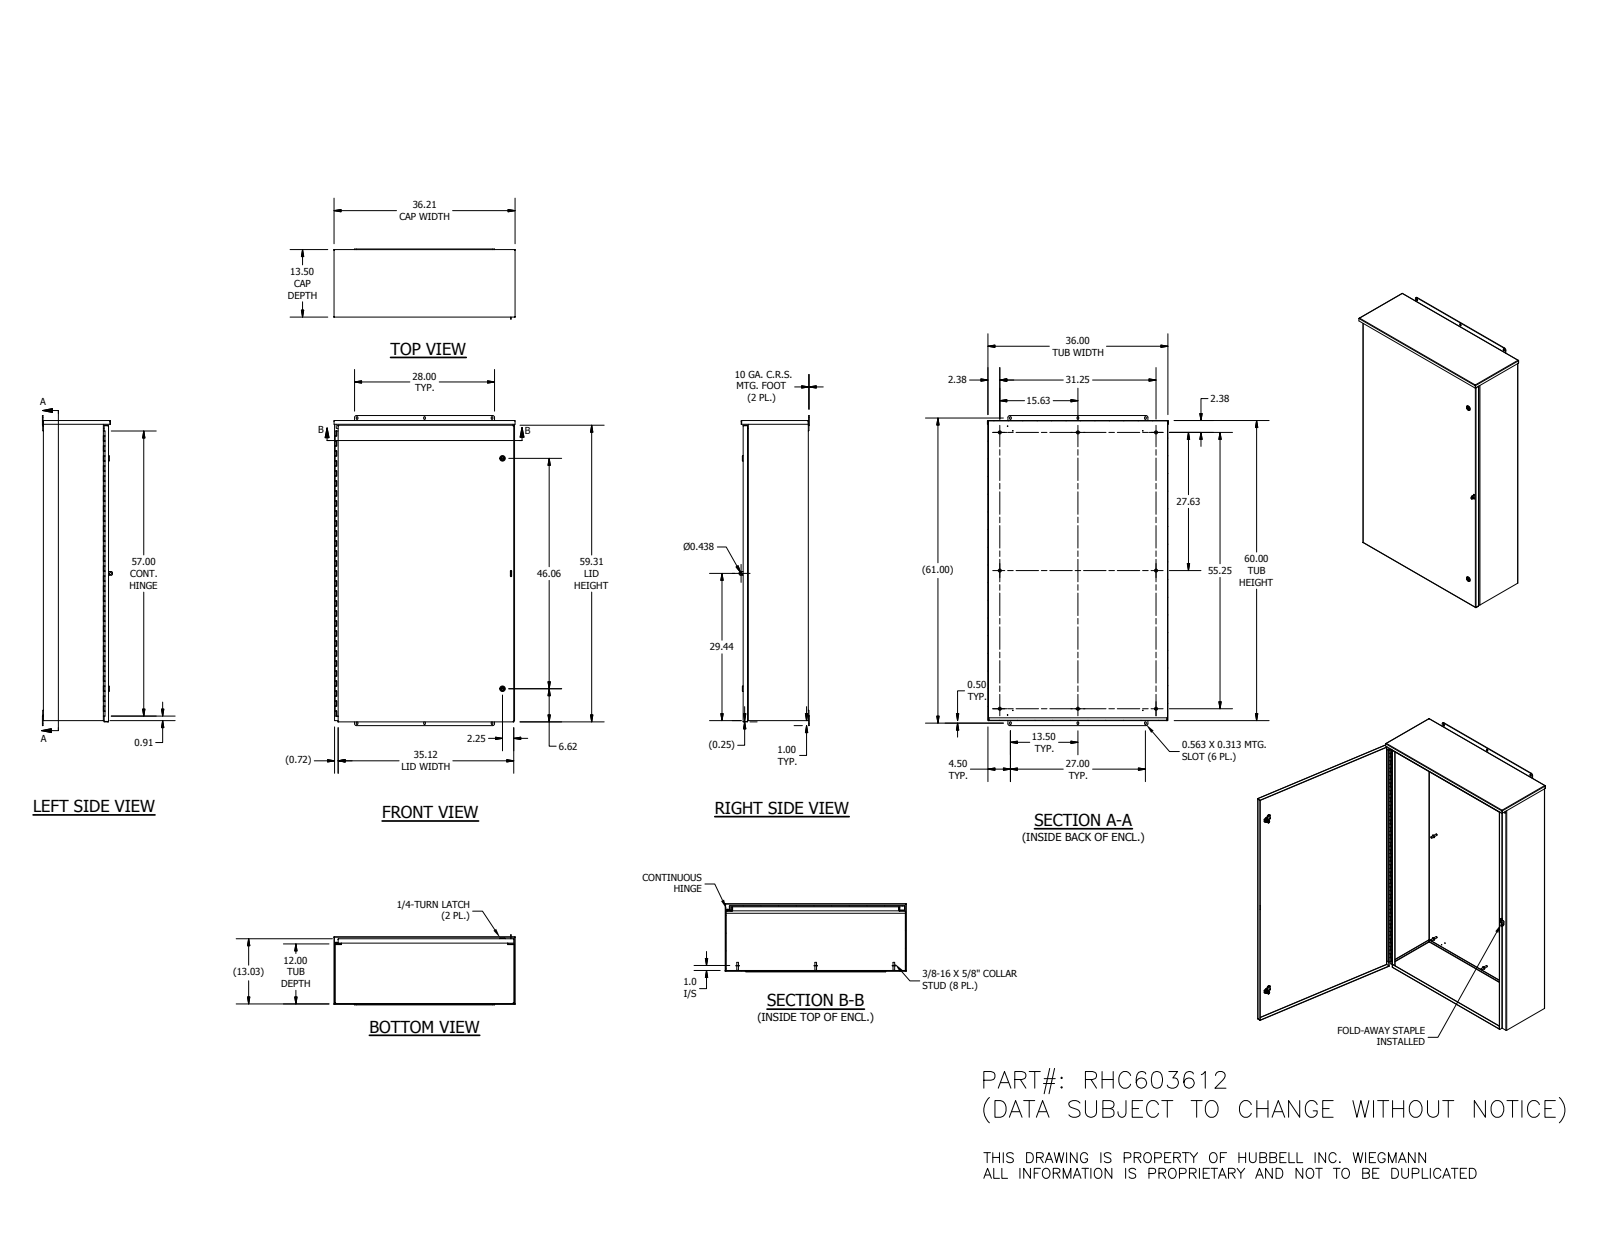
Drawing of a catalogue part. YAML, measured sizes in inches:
part_name: "RHC603612BLR; RHC36TOP; RHC3612BTM; RHC6036LID (+8 more)"
step_written_by: "Autodesk Inventor 2016 (AUTOMOTIVE_DESIGN)"
units: inches
bodies: {solids: 34, faces: 1778, planar: 1023, cylindrical: 603, other: 152}
overall_size: [62, 36.211, 14.012]
volume: 566.1
surface_area: 15190
round_holes:
  - {diameter: 0.12, count: 7}
  - {diameter: 0.125, count: 2}
  - {diameter: 0.197, count: 2}
  - {diameter: 0.315, count: 2}
  - {diameter: 0.394, count: 2}
  - {diameter: 0.402, count: 2}
  - {diameter: 0.634, count: 2}
  - {diameter: 0.802, count: 2}
  - {diameter: 0.198, count: 1}
  - {diameter: 0.201, count: 1}
  - {diameter: 0.437, count: 1}
round_bosses_or_shafts:
  - {diameter: 0.625, count: 8}
  - {diameter: 0.33, count: 8}
  - {diameter: 1.102, count: 2}
  - {diameter: 1.063, count: 2}
  - {diameter: 0.906, count: 2}
  - {diameter: 0.78, count: 2}
  - {diameter: 0.622, count: 2}
  - {diameter: 0.598, count: 2}
partial_cylinders:
  - {radius: 0.012, count: 56}
  - {radius: 0.02, count: 21}
  - {radius: 0.137, count: 13}
  - {radius: 0.156, count: 12}
  - {radius: 0.125, count: 10}
  - {radius: 0.031, count: 8}
  - {radius: 0.063, count: 8}
  - {radius: 0.105, count: 8}
face_to_face_distances: [0.074, 12.959, 13.033, 12.885, 35.926, 59.926, 35.852, 36, 59.852, 60]
hole_center_spacings: [1.414, 26, 27.076, 55.88, 56.825, 61.633, 62.93, 0.354]
